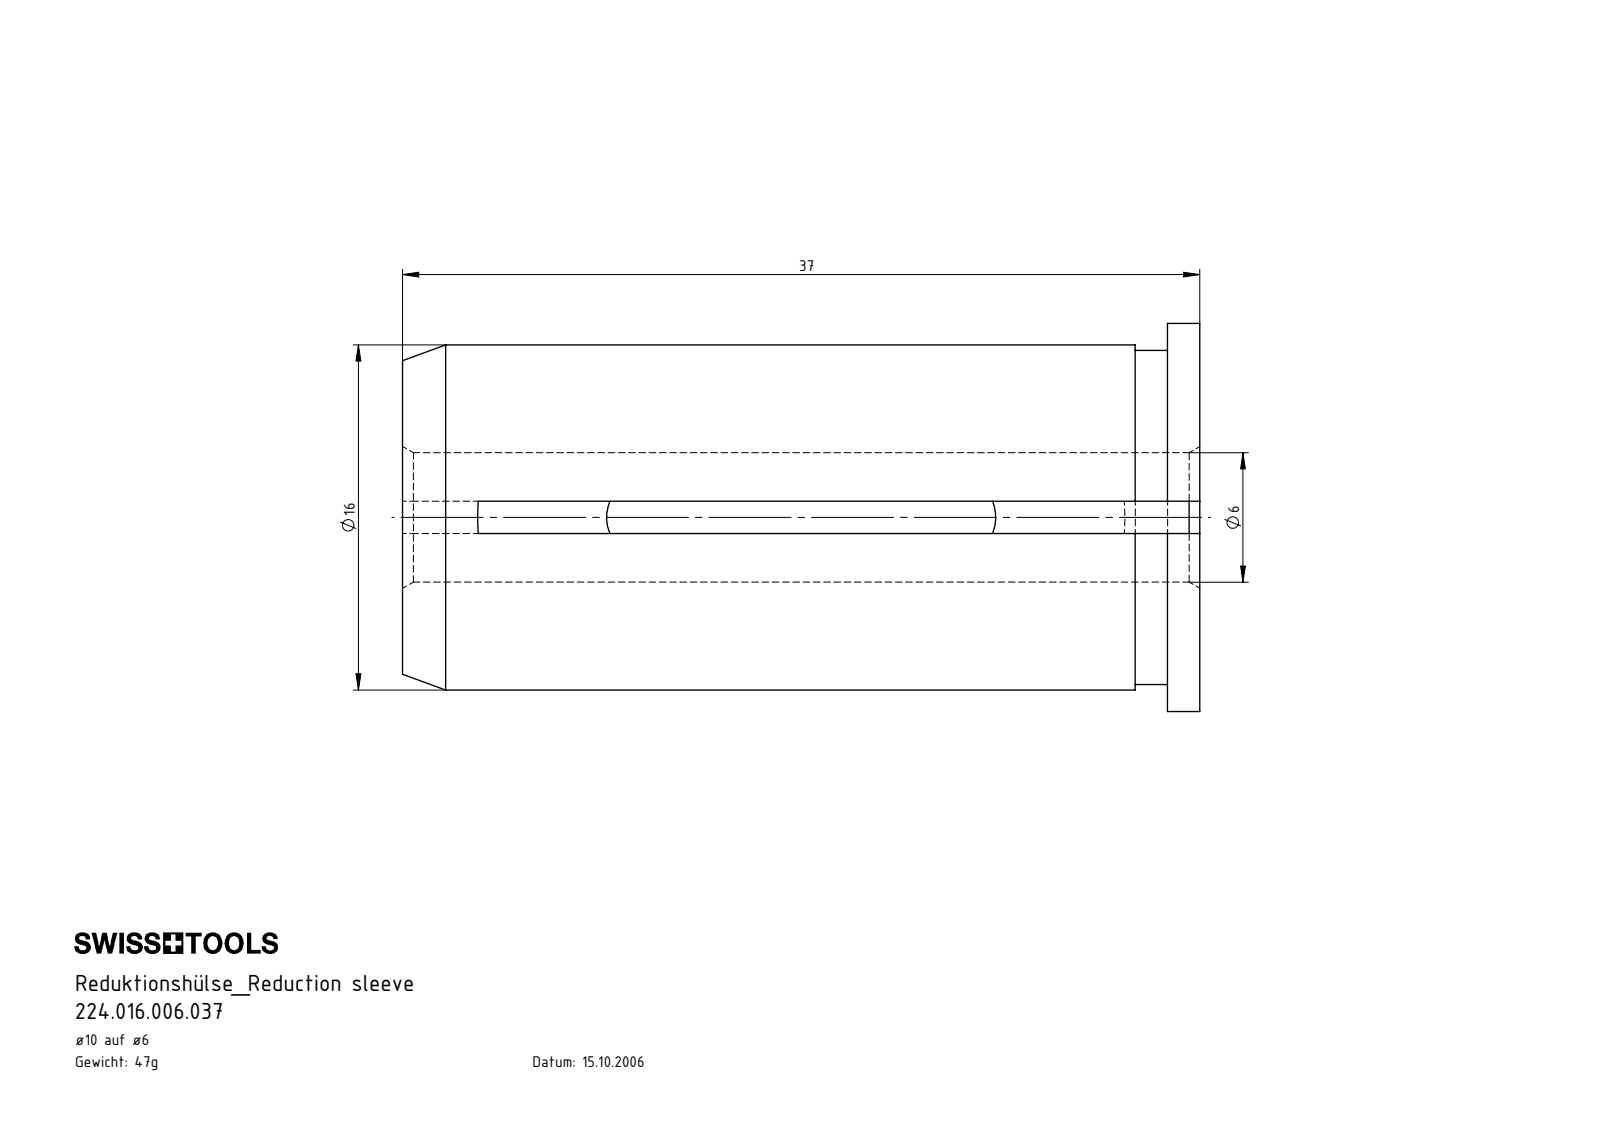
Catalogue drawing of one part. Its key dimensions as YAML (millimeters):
part_name: "U06.U16.001.037"
step_written_by: "SolidWorks 2017 (AUTOMOTIVE_DESIGN)"
units: millimeters
bodies: {solids: 1, faces: 17, planar: 8, cylindrical: 6, other: 3}
overall_size: [37, 18, 17.97]
volume: 5953
surface_area: 3445
round_holes:
  - {diameter: 6, count: 1}
round_bosses_or_shafts:
  - {diameter: 18, count: 1}
  - {diameter: 16, count: 1}
  - {diameter: 15.5, count: 1}
partial_cylinders:
  - {radius: 31.5, count: 2}
face_to_face_distances: [1.5, 37, 35.5, 34, 3]
